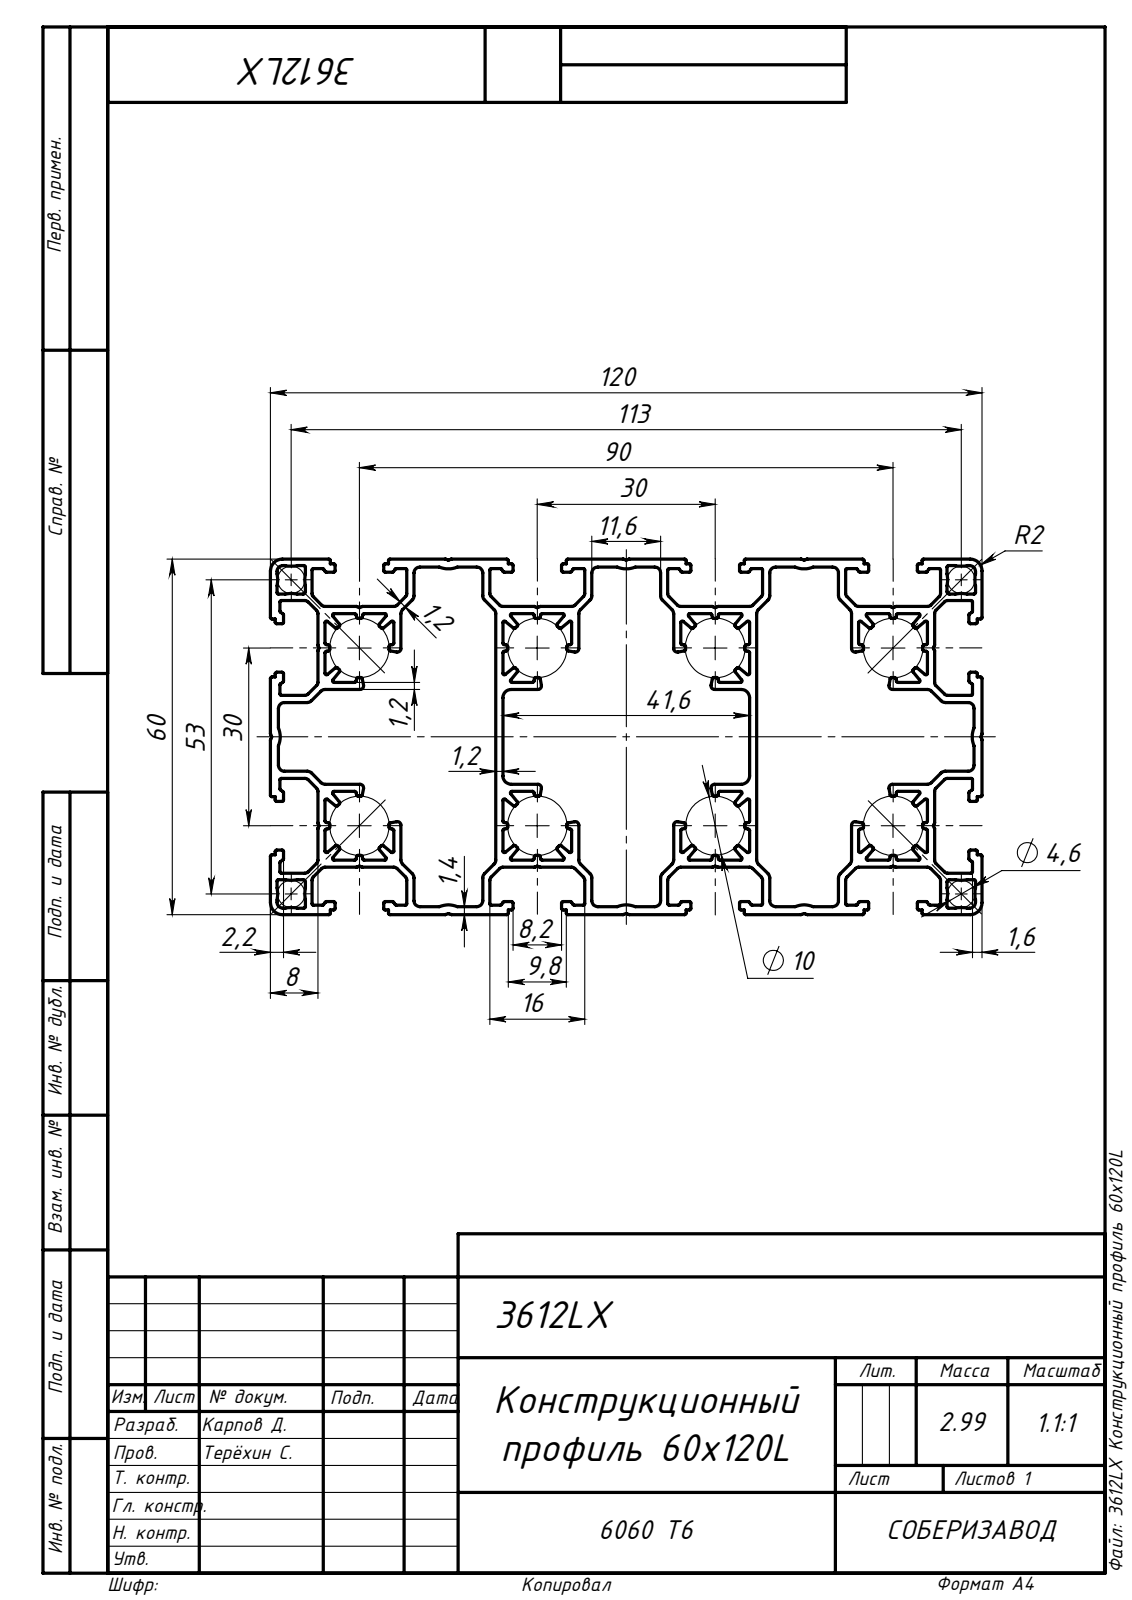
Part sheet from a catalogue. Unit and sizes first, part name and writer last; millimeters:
Units: millimetres
Overall size (bounding box): 1000 × 120 × 60
Partial cylindrical surfaces — rounded edges, fillets, slot ends (radius × count): R0.25 ×400, R1 ×52, R0.75 ×48, R0.6 ×16, R5.05 ×16, R4 ×8, R5 ×8, R0.4 ×4
Main face-to-face distances: 30, 1.2, 60, 42.8, 8, 15, 12.8, 44, 38, 52
Volume: 1 109 000 mm³ · Surface area: 1 644 000 mm²
Bodies: 1 solid, 1246 faces (542 planar, 704 cylindrical, 0 other)
STEP written by: SolidWorks 2019 (AUTOMOTIVE_DESIGN)
